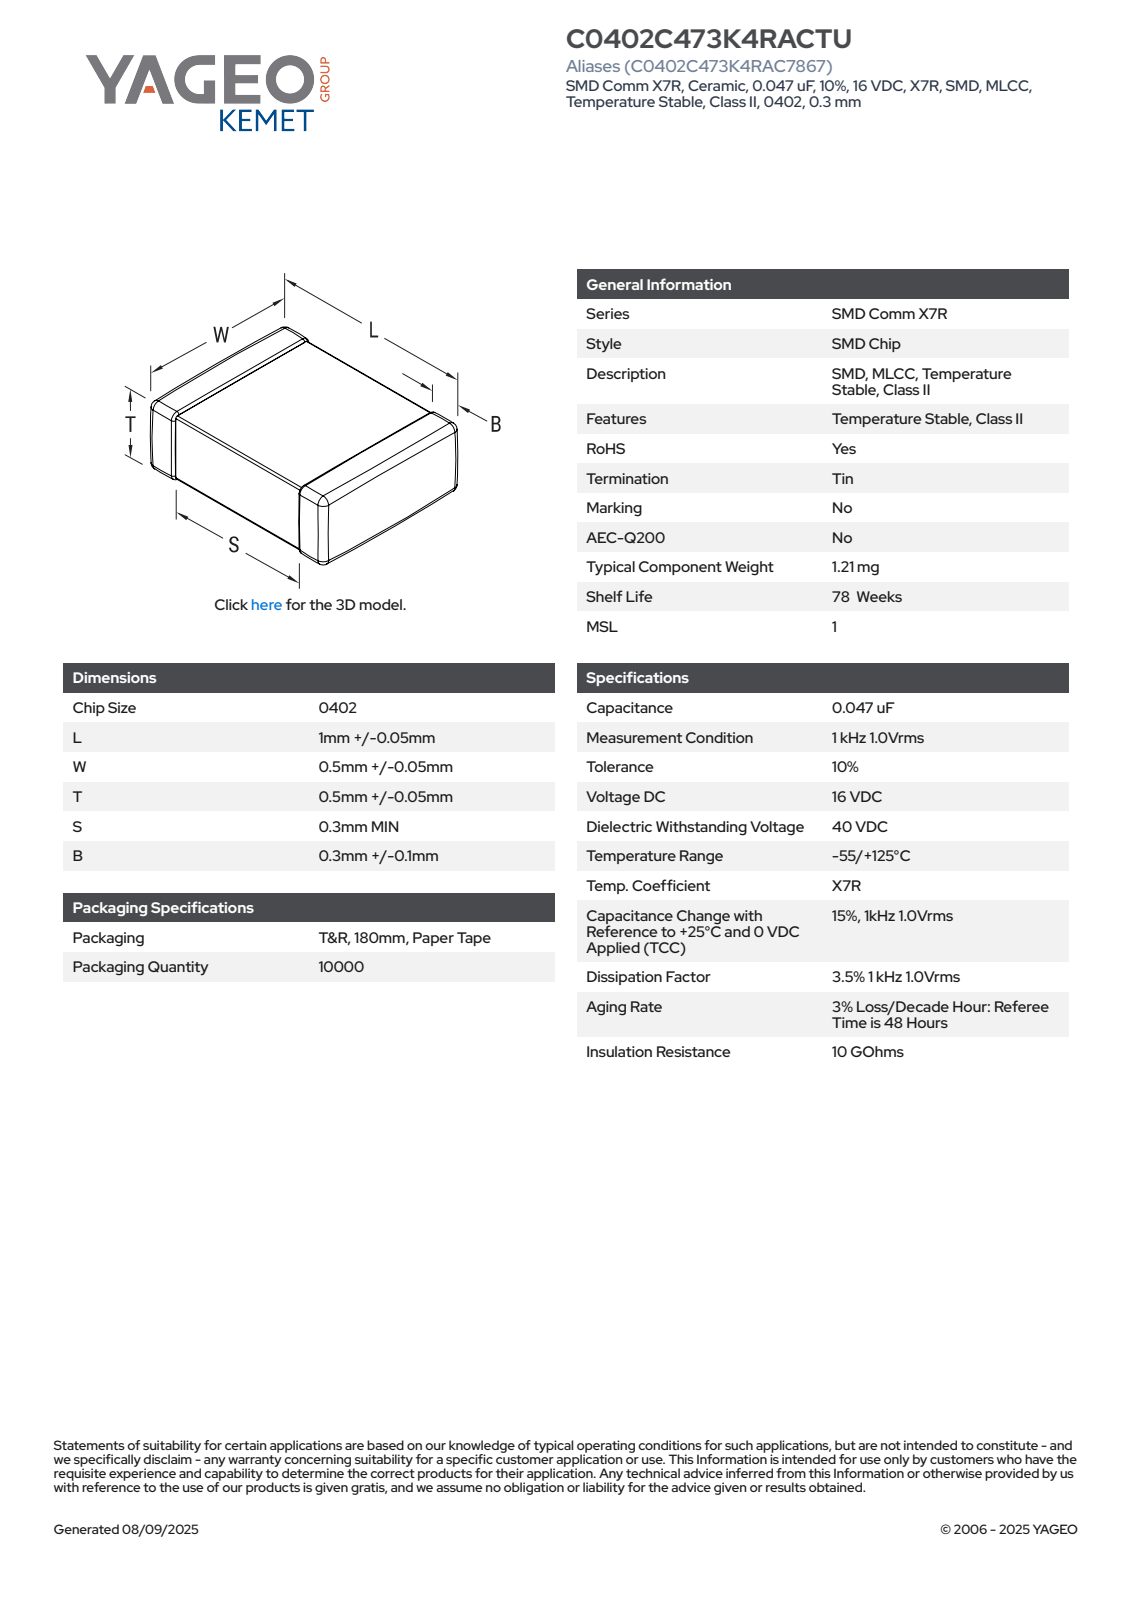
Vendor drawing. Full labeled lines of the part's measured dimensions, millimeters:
Part name (STEP PRODUCT): CCS_CCSTD_0402_L1.05W0.55T0.55B0.3
STEP written by: SolidWorks 2014 (AUTOMOTIVE_DESIGN)
Units: millimetres
Bodies: 4 solids, 125 faces (71 planar, 38 cylindrical, 16 other)
Overall size (bounding box): 1.05 × 0.55 × 0.55
Volume: 0.306 mm³ · Surface area: 3 mm²
Main face-to-face distances: 0.54, 0.55, 0.53, 1.05, 0.49, 0.56, 0.57, 0.48, 0.5, 0.52
